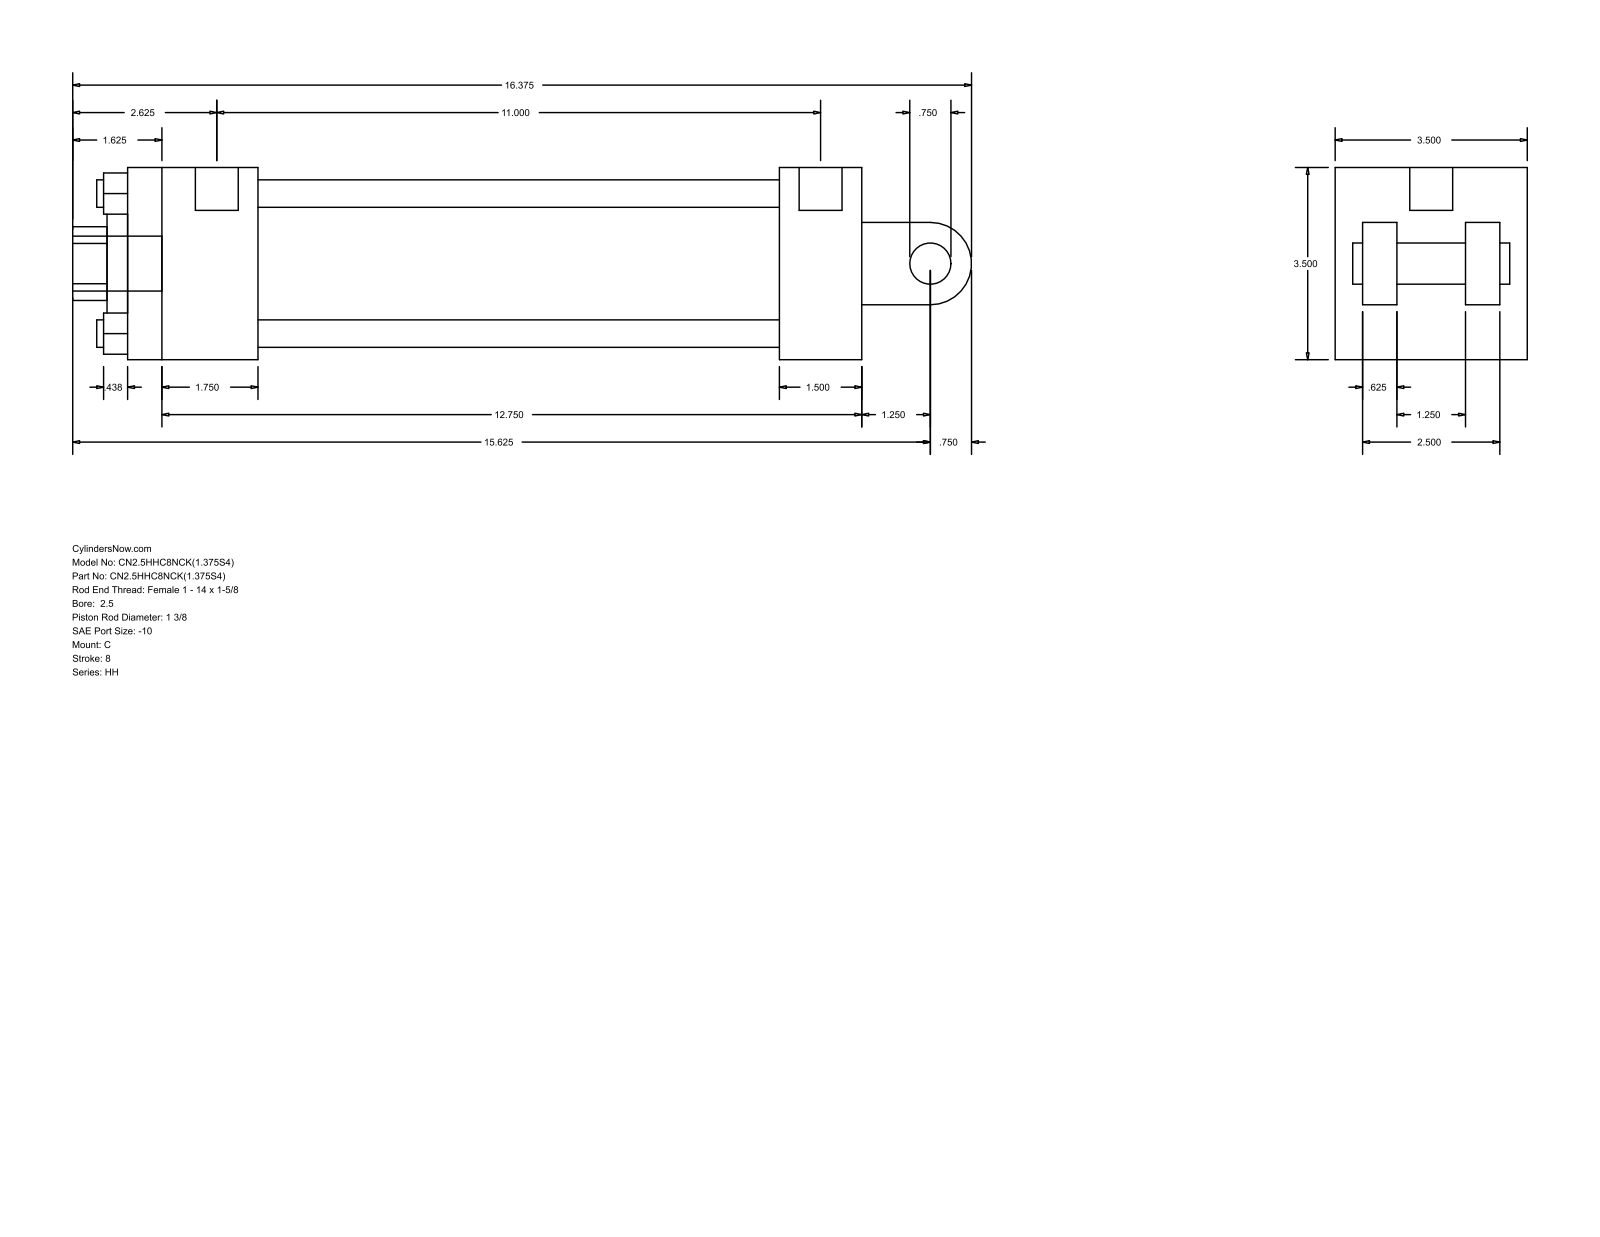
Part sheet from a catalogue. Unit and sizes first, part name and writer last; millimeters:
Units: millimetres
Overall size (bounding box): 415.93 × 88.9 × 88.9
Round holes (diameter × count): ⌀12.7 ×4, ⌀5.56 ×2, ⌀19.84 ×1, ⌀34.92 ×1, ⌀50.8 ×1, ⌀73.03 ×1
Round bosses / shafts (diameter × count): ⌀5.56 ×2, ⌀25.4 ×1, ⌀19.84 ×1, ⌀19.05 ×1
Partial cylindrical surfaces — rounded edges, fillets, slot ends (radius × count): R17.06 ×1, R19.05 ×1
Main face-to-face distances: 88.9, 339.72, 38.1, 63.5, 15.87, 12.7, 301.62, 60.32, 241.3, 279.4
Hole centre spacings: 45.79, 64.76, 91.58, 1.59
Bodies: 0 solids, 99 faces (70 planar, 29 cylindrical, 0 other)
Part name (STEP PRODUCT): HH_C__0250_1.375
STEP written by: GSSL Pune (CONFIG_CONTROL_DESIGN)
